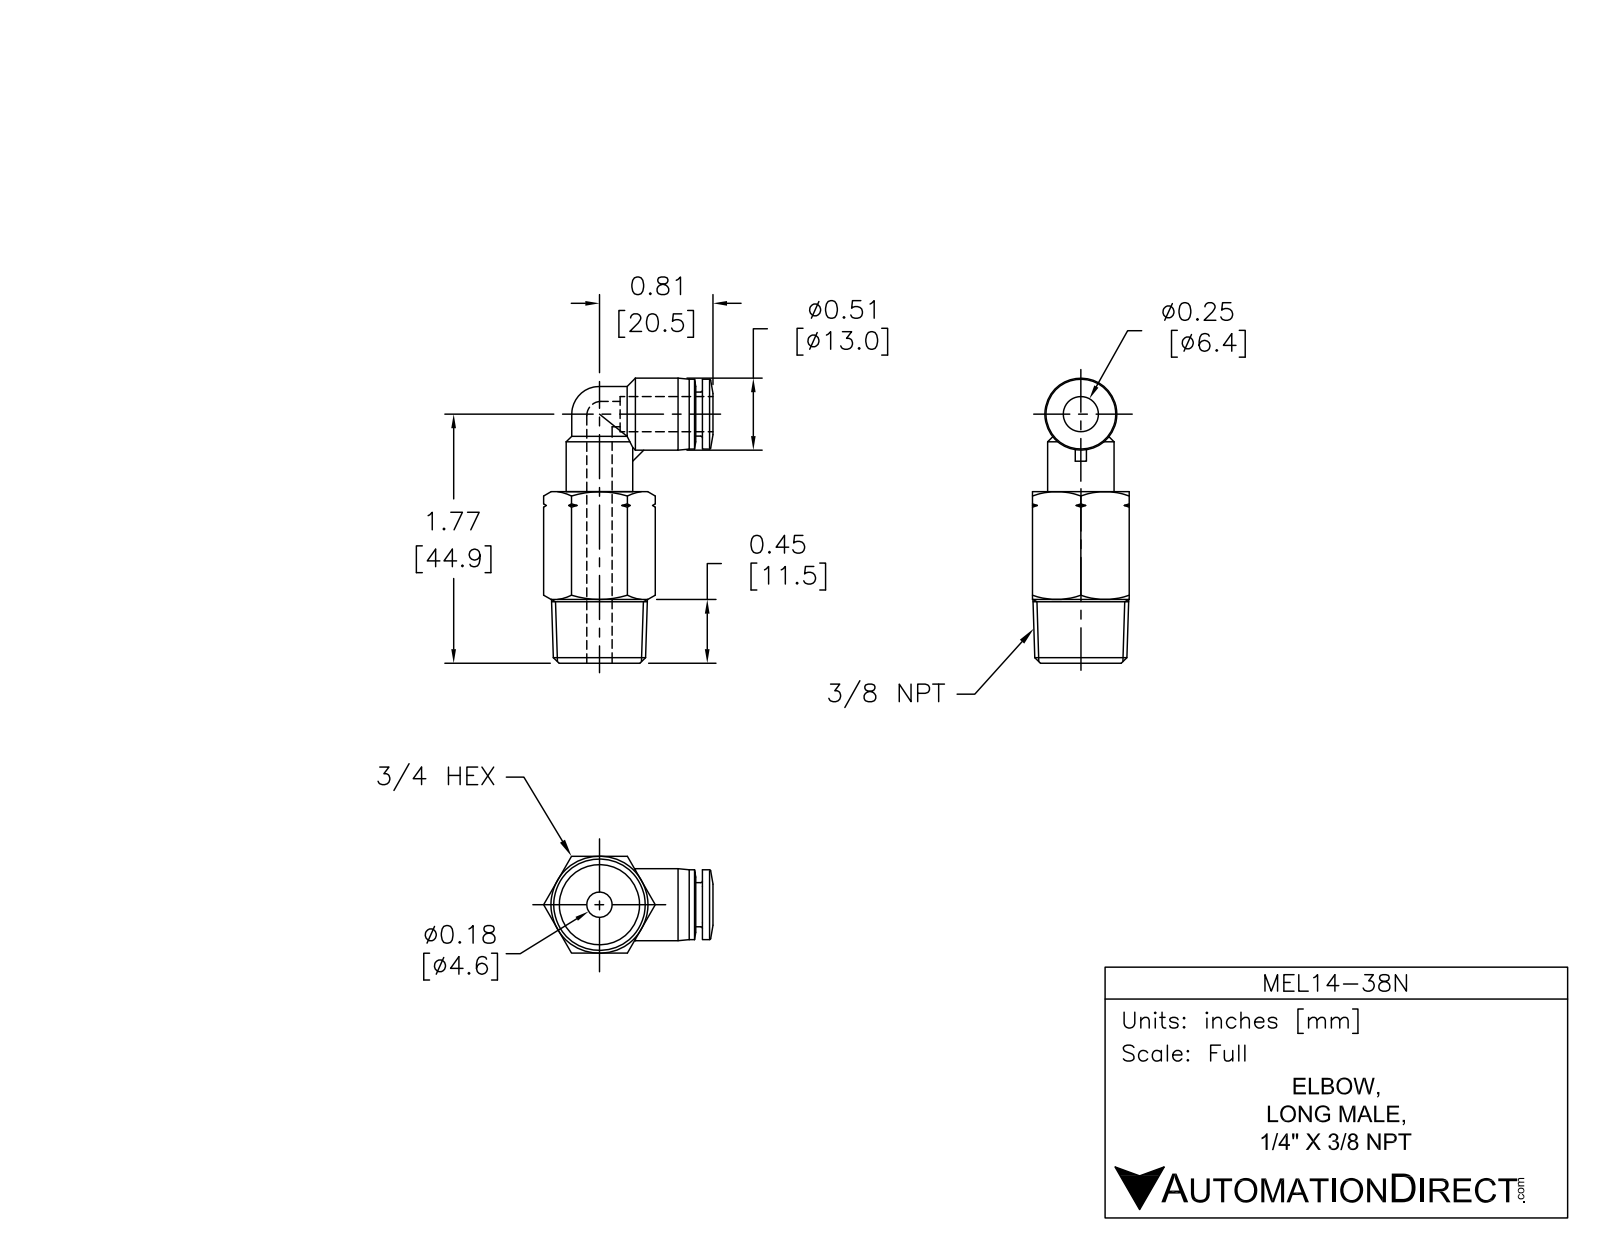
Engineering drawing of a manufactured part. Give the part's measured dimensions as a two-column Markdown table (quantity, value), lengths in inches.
| quantity | value |
| --- | --- |
| part name | MEL14-38N |
| STEP written by | SolidWorks 2015 (AUTOMOTIVE_DESIGN) |
| units | inches |
| bodies | 1 solid, 88 faces (15 planar, 20 cylindrical, 53 other) |
| overall size | 2.028 × 1.204 × 0.687 |
| volume | 0.611 in³ |
| surface area | 7.183 in² |
| round holes (diameter × count) | 0.177 × 2, 0.258 × 1 |
| round bosses / shafts (diameter × count) | 0.394 × 2, 0.512 × 1, 0.496 × 1, 0.472 × 1, 0.313 × 1 |
| main face-to-face distances | 0.687, 1.22, 0.047, 0.539, 0.587, 0.304, 0.383, 0.453, 0.768, 0.079 |
